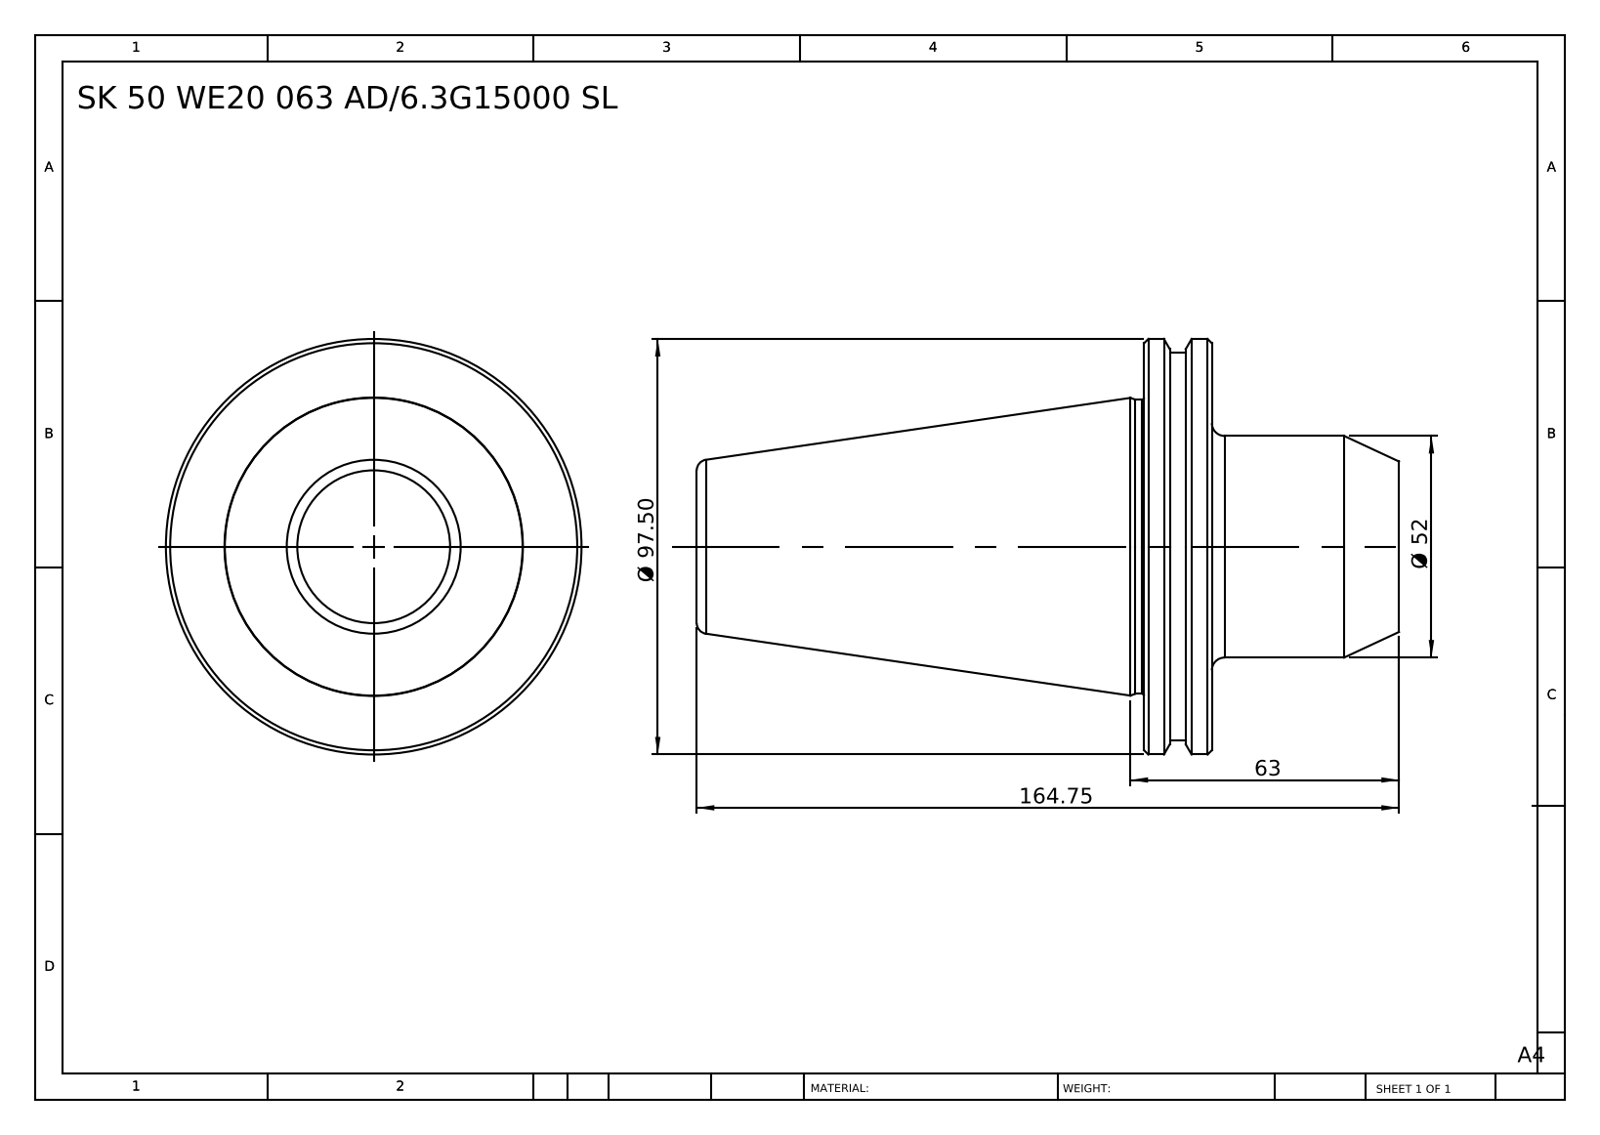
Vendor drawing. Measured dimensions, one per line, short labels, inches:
name: SK50 WE20 063 AD-6.3G15000 SL
written by: SolidWorks 2014 (CONFIG_CONTROL_DESIGN)
unit: in
bodies: 1 solid, 36 faces (6 planar, 10 cylindrical, 20 other)
size: 6.486 × 3.839 × 3.839
volume: 28.14 in³; area: 66 in²
bosses: 1× ⌀3.839, 1× ⌀3.583, 1× ⌀2.717, 1× ⌀2.047
face distances: 0.626, 1.728, 2.354, 6.486, 4.758, 4.132, 1.969, 0.241, 0.385, 4.517
